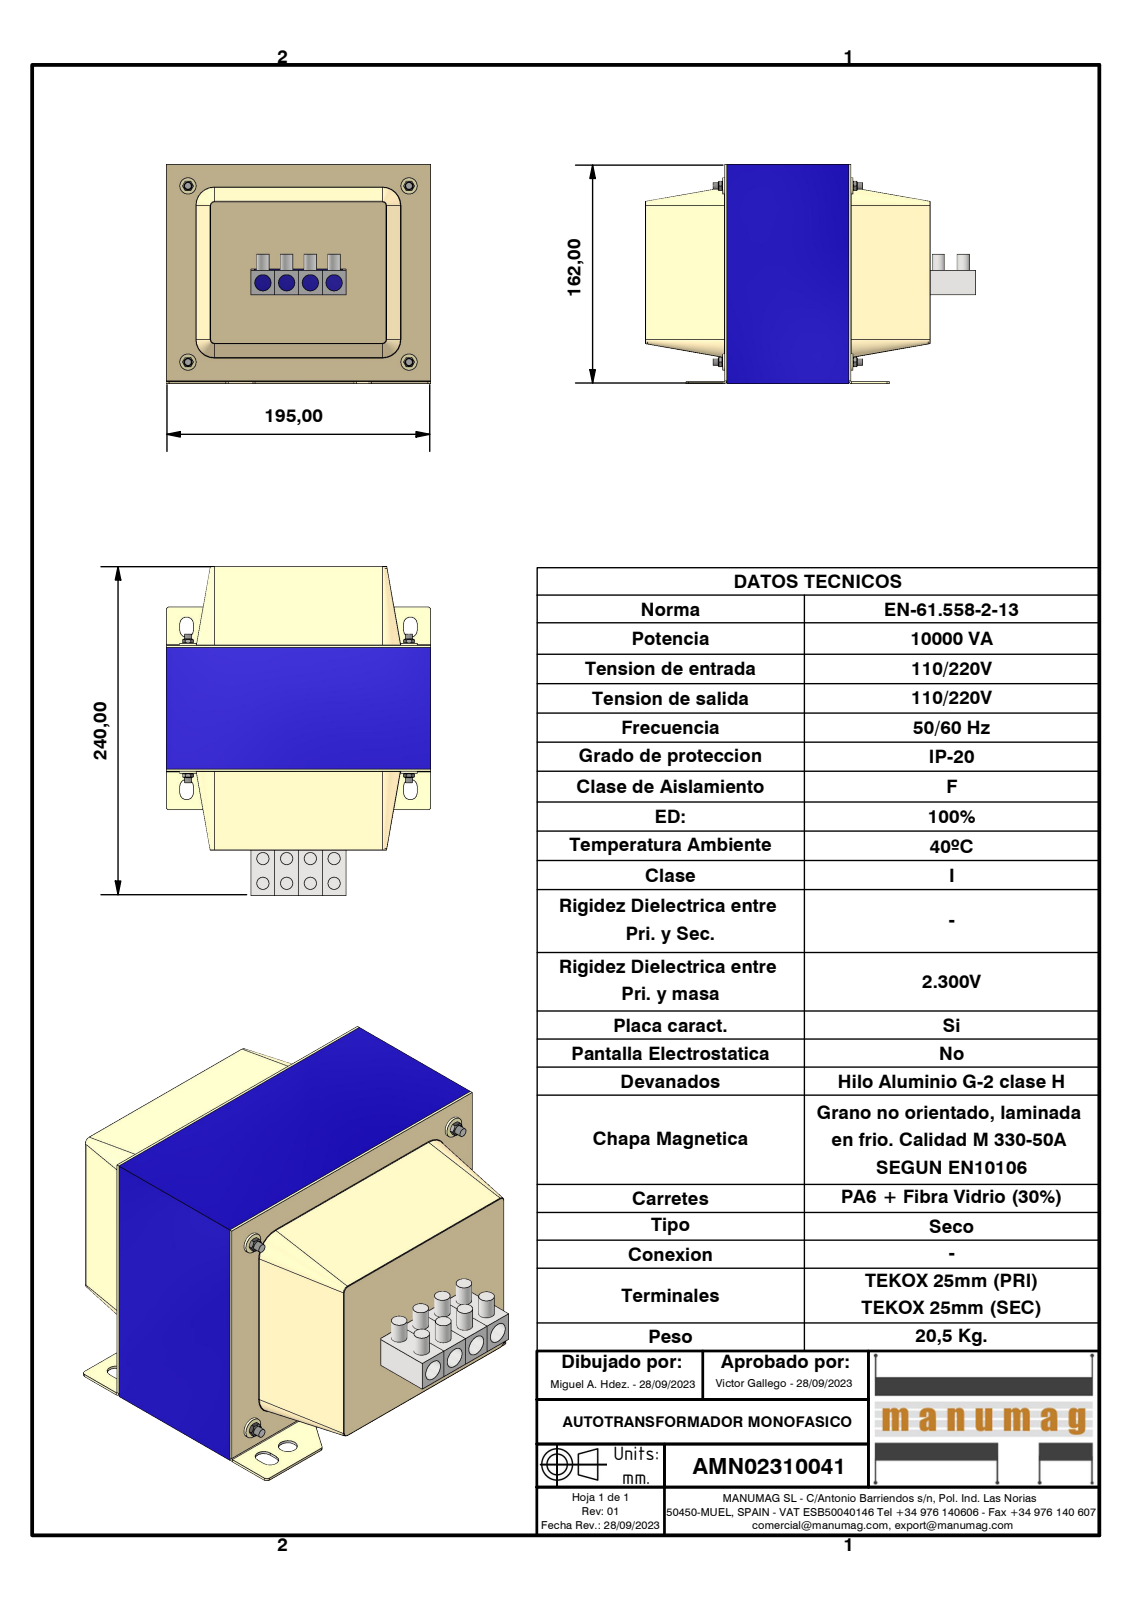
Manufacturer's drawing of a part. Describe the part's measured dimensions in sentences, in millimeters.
The part is named "AMN02310041; EI195 x 162 - 90 (Rc65) Azul; TAPA RC65 VENTANA 4 ELEMENTOS 25; TAPA RC65 CIEGA (+5 more)". Its 3-D file was written by "Autodesk Inventor 2023 (AUTOMOTIVE_DESIGN)". It is 27 solids with 374 faces: 198 planar, 104 cylindrical and 72 other. Overall it measures 243.5 by 195 by 162 millimeters. Its volume is 2 380 000 cubic millimeters and its surface area 438 525 square millimeters. Round holes: 8 of diameter 11, 4 of diameter 3.24, 4 of diameter 5, 4 of diameter 9, 4 of diameter 12. Round bosses or shafts: 8 of diameter 9, 4 of diameter 12, 4 of diameter 5.9. Partial cylindrical surfaces (rounded edges, fillets, slot ends): 16 of radius 0.38, 14 of radius 2, 8 of radius 5, 2 of radius 0.5. The main face-to-face distances are 1.5, 58.5, 150, 130, 32.5, 90, 65, 148.5, 60, 57. The hole center spacings are 17.5, 35, 80.47, 90.36, 93.35, 102, 107.55, 115.14.
